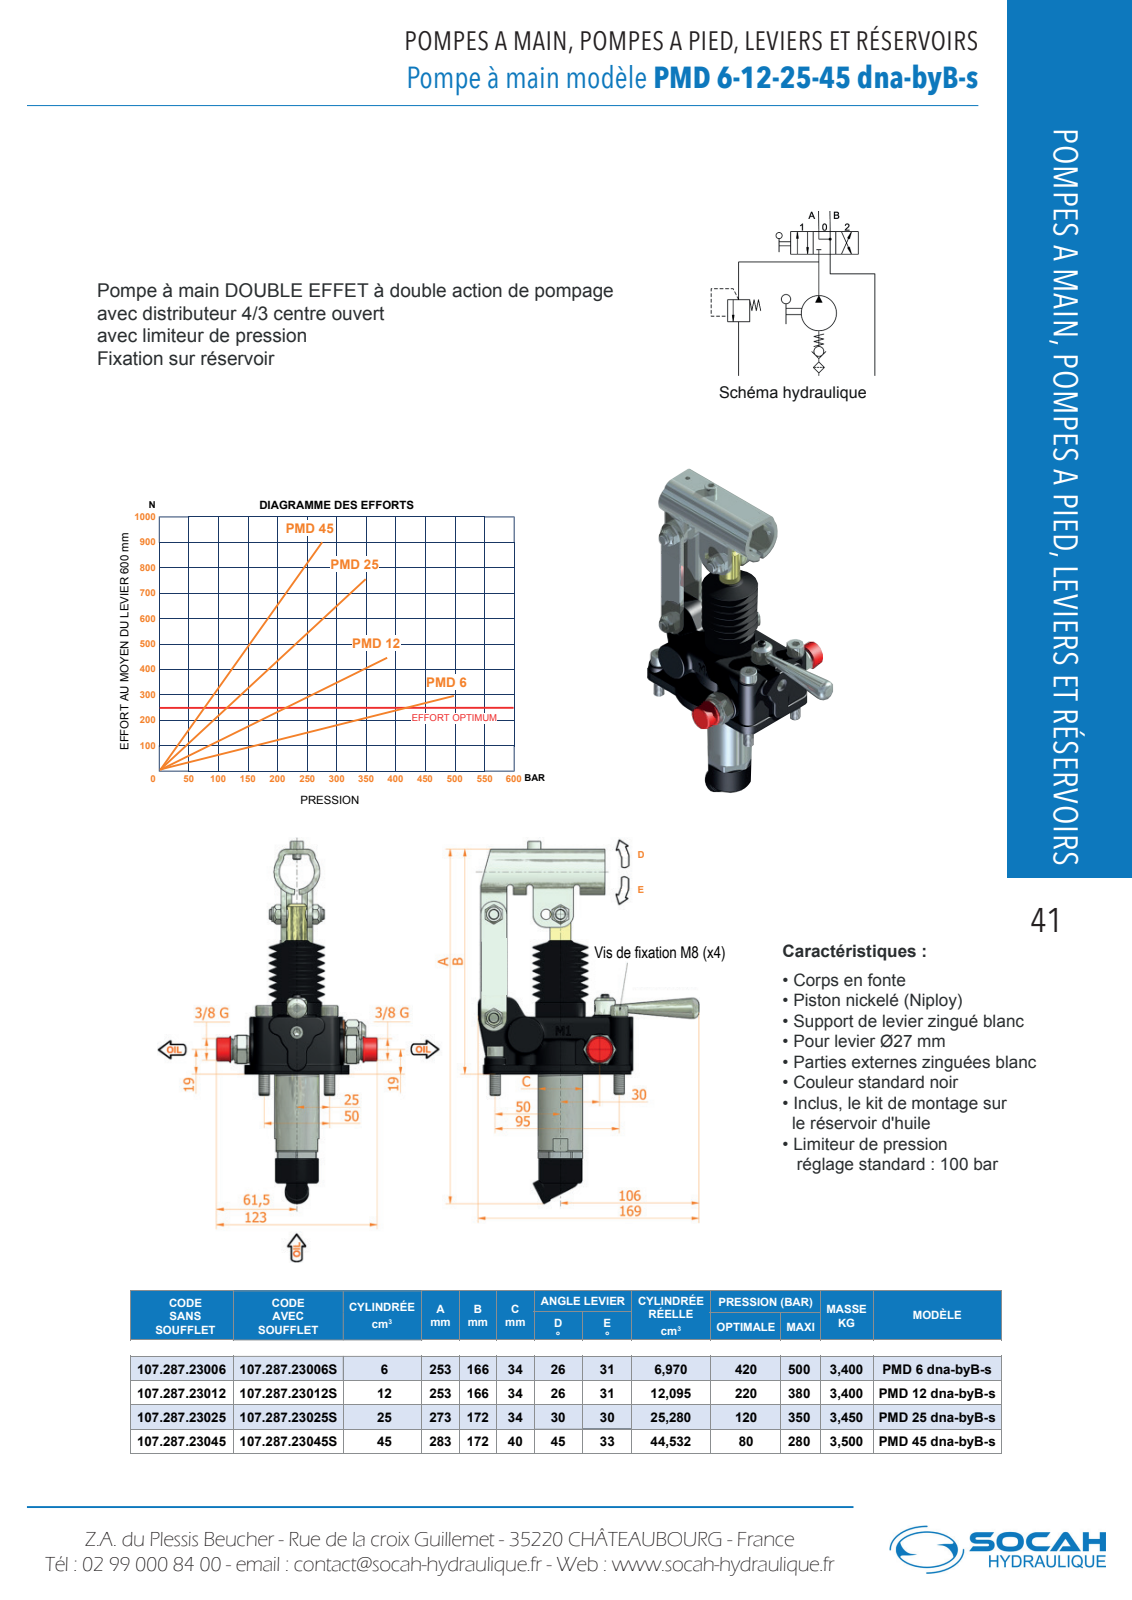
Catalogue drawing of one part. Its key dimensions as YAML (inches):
part_name: "6056.0046.10.50 Derivazione 2"
step_written_by: "Autodesk Inventor 2013 (AUTOMOTIVE_DESIGN)"
units: inches
bodies: {solids: 17, faces: 1555, planar: 716, cylindrical: 348, other: 491}
overall_size: [10.939, 6.654, 4.843]
volume: 20.03
surface_area: 236.8
round_holes:
  - {diameter: 0.315, count: 6}
  - {diameter: 0.551, count: 4}
  - {diameter: 0.197, count: 3}
  - {diameter: 0.194, count: 2}
  - {diameter: 0.157, count: 1}
  - {diameter: 0.354, count: 1}
  - {diameter: 0.394, count: 1}
  - {diameter: 0.413, count: 1}
  - {diameter: 0.531, count: 1}
  - {diameter: 0.63, count: 1}
  - {diameter: 0.669, count: 1}
  - {diameter: 0.787, count: 1}
round_bosses_or_shafts:
  - {diameter: 0.512, count: 4}
  - {diameter: 0.472, count: 4}
  - {diameter: 0.335, count: 4}
  - {diameter: 0.787, count: 3}
  - {diameter: 0.709, count: 3}
  - {diameter: 0.435, count: 3}
  - {diameter: 0.315, count: 3}
  - {diameter: 0.236, count: 3}
partial_cylinders:
  - {radius: 0.039, count: 30}
  - {radius: 0.008, count: 24}
  - {radius: 0.004, count: 16}
  - {radius: 0.197, count: 16}
  - {radius: 0.079, count: 14}
  - {radius: 0.118, count: 9}
  - {radius: 0.315, count: 9}
  - {radius: 0.014, count: 6}
face_to_face_distances: [0.157, 0.787, 0.197, 0.079, 0.63, 1.457, 1.732, 0.039, 1.654, 0.276]
hole_center_spacings: [1.004, 1.075, 1.969, 2.027, 2.201, 3.45, 3.678, 3.74]
